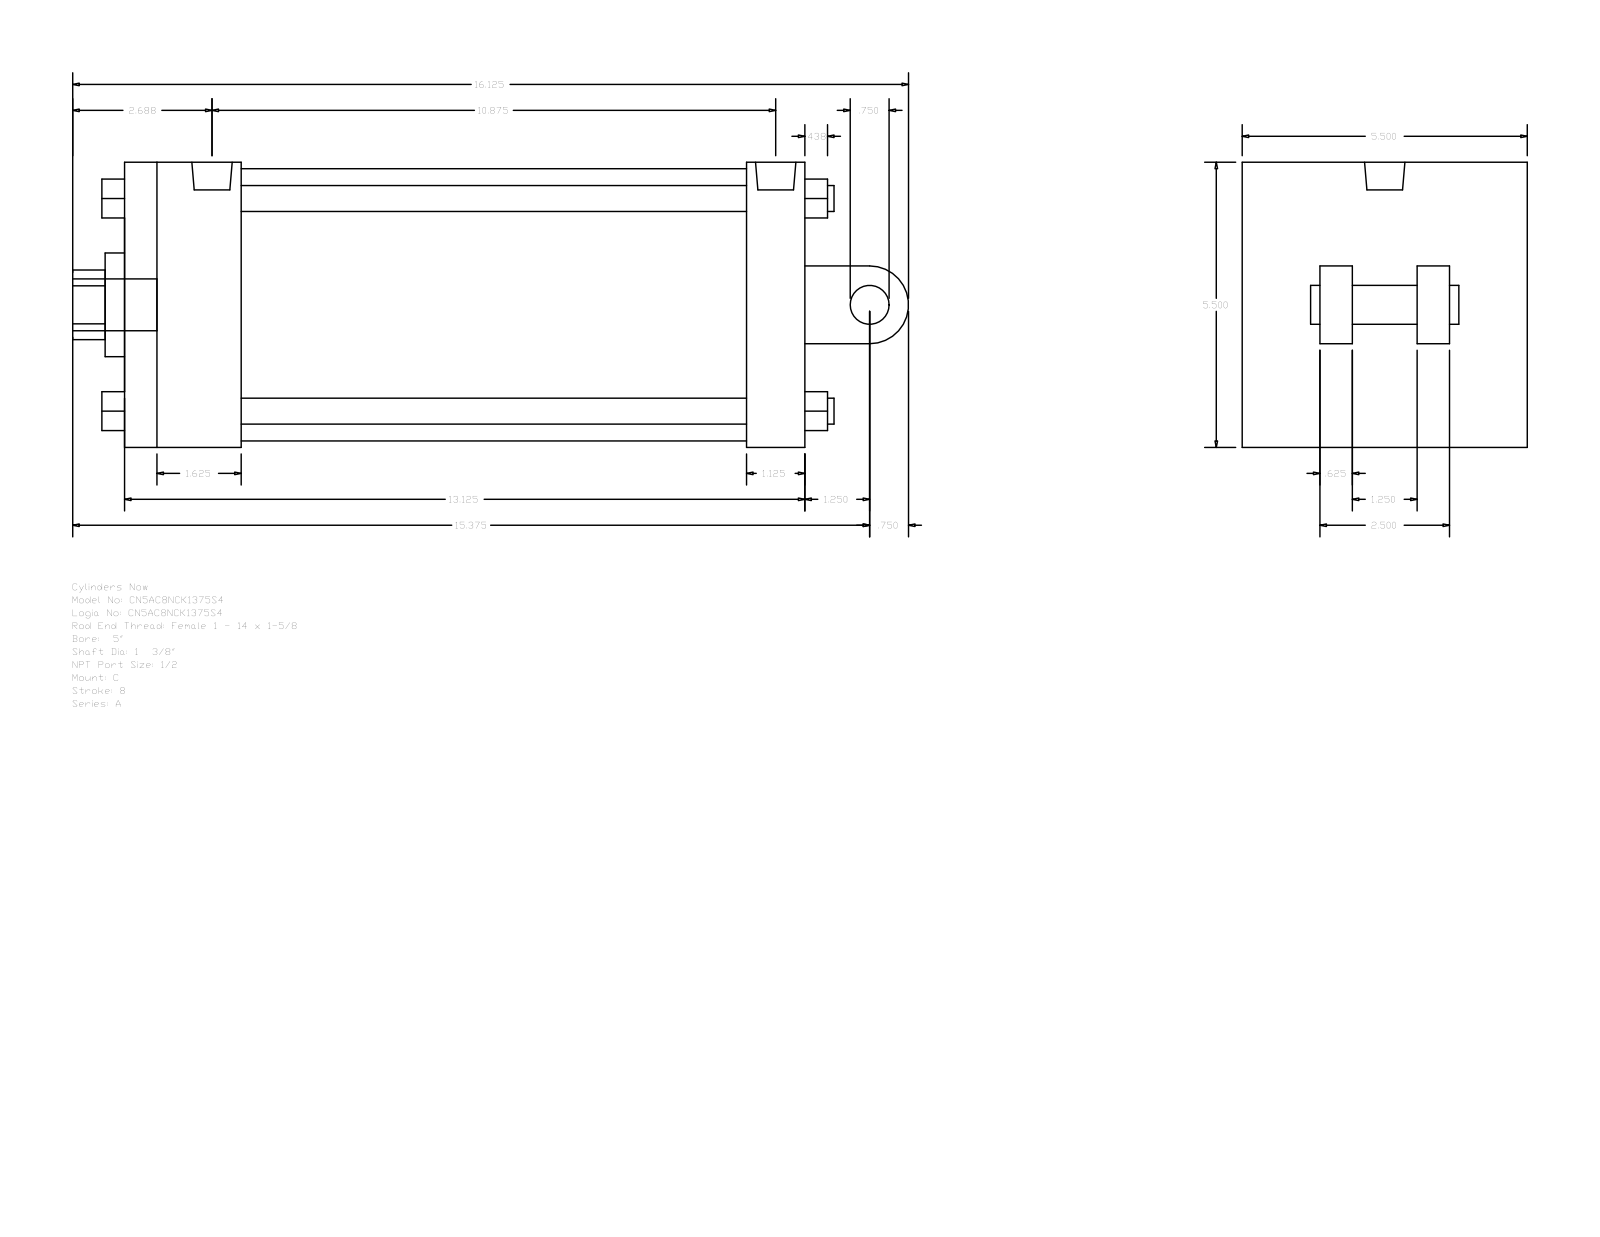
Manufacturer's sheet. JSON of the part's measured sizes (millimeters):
{"part_name": "A_C__0500_1.375", "step_written_by": "GSSL Pune (CONFIG_CONTROL_DESIGN)", "units": "millimeters", "bodies": {"solids": 0, "faces": 135, "planar": 102, "cylindrical": 33, "other": 0}, "overall_size": [409.57, 139.7, 139.7], "round_holes": [[8.73, 2], [19.77, 1], [34.92, 1], [50.8, 1], [133.35, 1]], "round_bosses_or_shafts": [[12.7, 4], [8.73, 2], [25.4, 1], [19.77, 1], [19.05, 1]], "partial_cylinders_radius": [[17.06, 1], [19.05, 1]], "face_to_face_distances": [139.7, 333.37, 28.57, 57.15, 304.8, 247.65, 276.22, 38.1, 15.87, 101.6], "hole_center_spacings": [2.39]}
